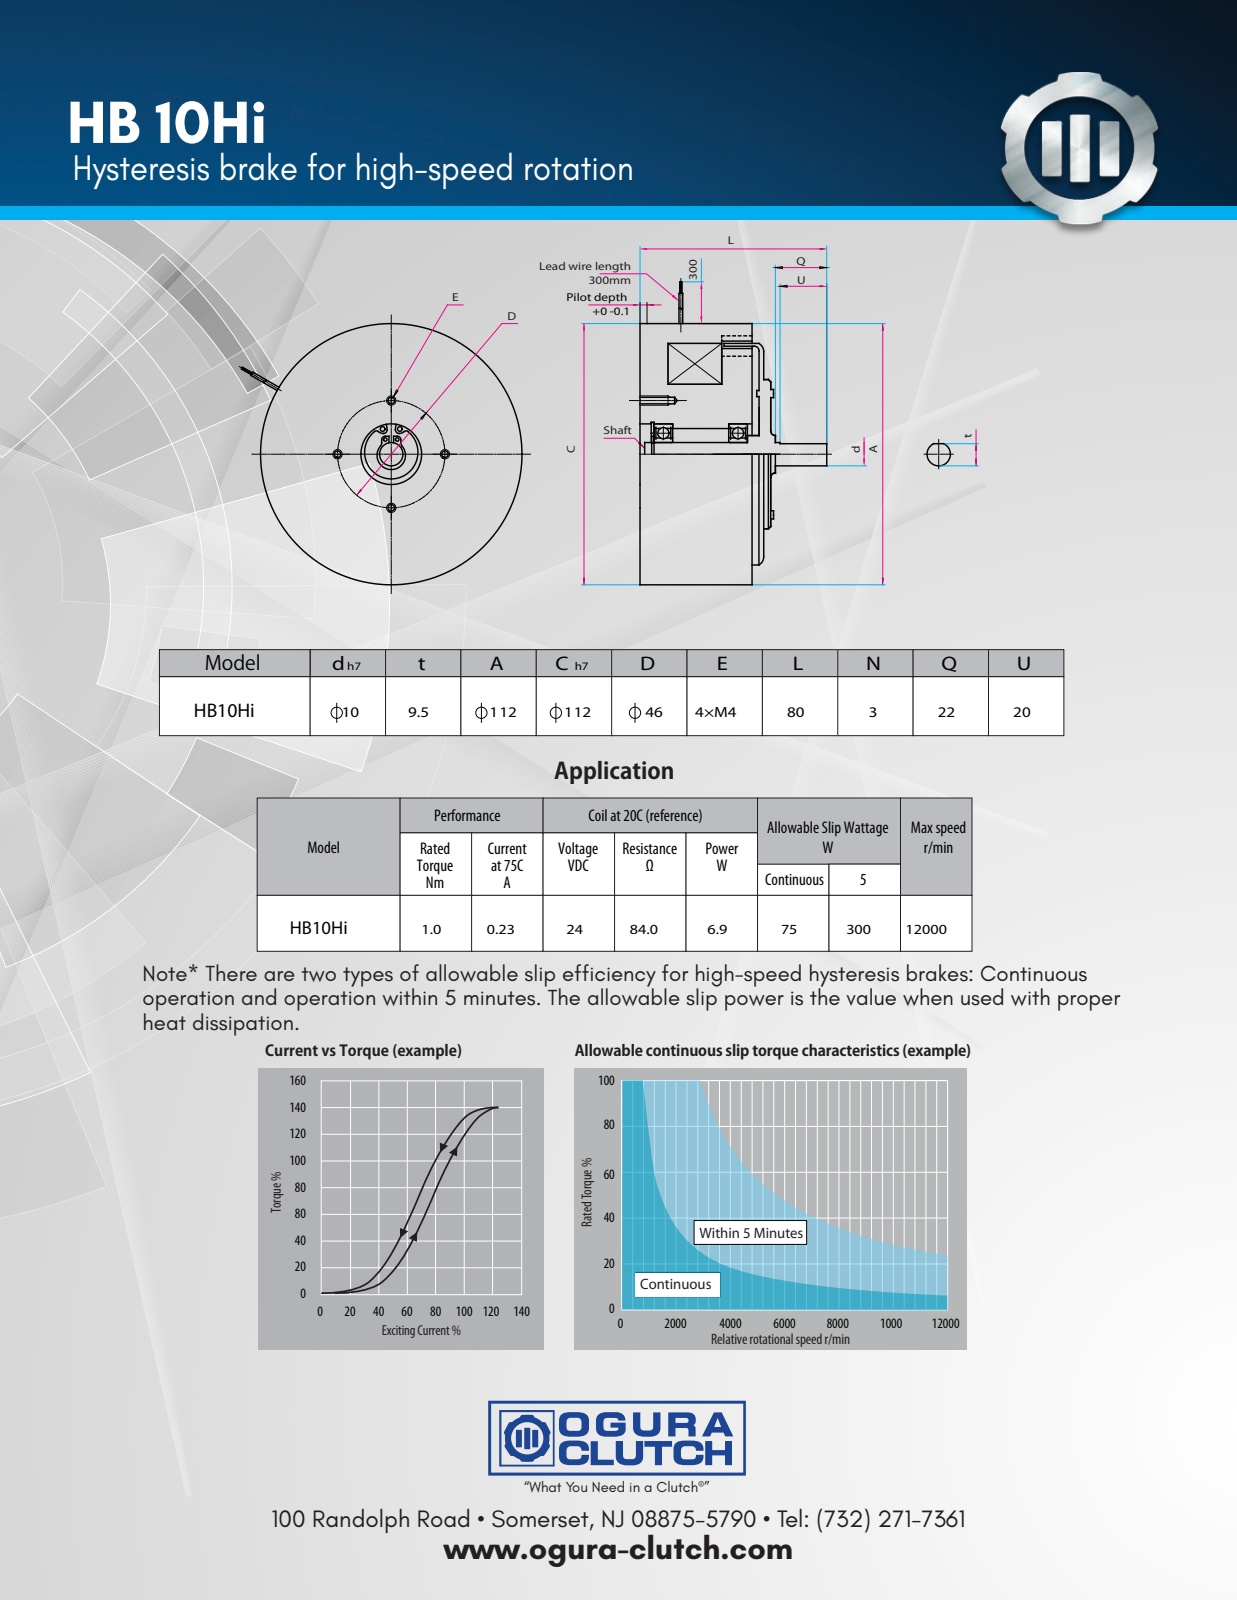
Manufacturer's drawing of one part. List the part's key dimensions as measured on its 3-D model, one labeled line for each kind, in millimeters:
Part name (STEP PRODUCT): HB10
STEP written by: SolidWorks 2018 (CONFIG_CONTROL_DESIGN)
Units: millimetres
Bodies: 1 solid, 247 faces (65 planar, 147 cylindrical, 35 other)
Overall size (bounding box): 140.75 × 136 × 80
Volume: 532 802 mm³ · Surface area: 60 741 mm²
Round holes (diameter × count): ⌀5.5 ×6, ⌀8 ×4, ⌀1.2 ×2, ⌀22 ×1
Round bosses / shafts (diameter × count): ⌀7 ×4, ⌀1.5 ×2, ⌀1.2 ×2, ⌀136 ×1, ⌀112 ×1, ⌀95 ×1, ⌀92 ×1, ⌀64 ×1
Partial cylindrical surfaces — rounded edges, fillets, slot ends (radius × count): R3 ×30, R0.5 ×2, R2.04 ×2, R4.8 ×1, R47.8 ×1
Main face-to-face distances: 3, 5, 8, 53, 45, 48, 50, 56, 40, 27
Hole centre spacings: 62, 23, 32.53, 43.62, 54.28, 66.13, 76.15, 82.72
